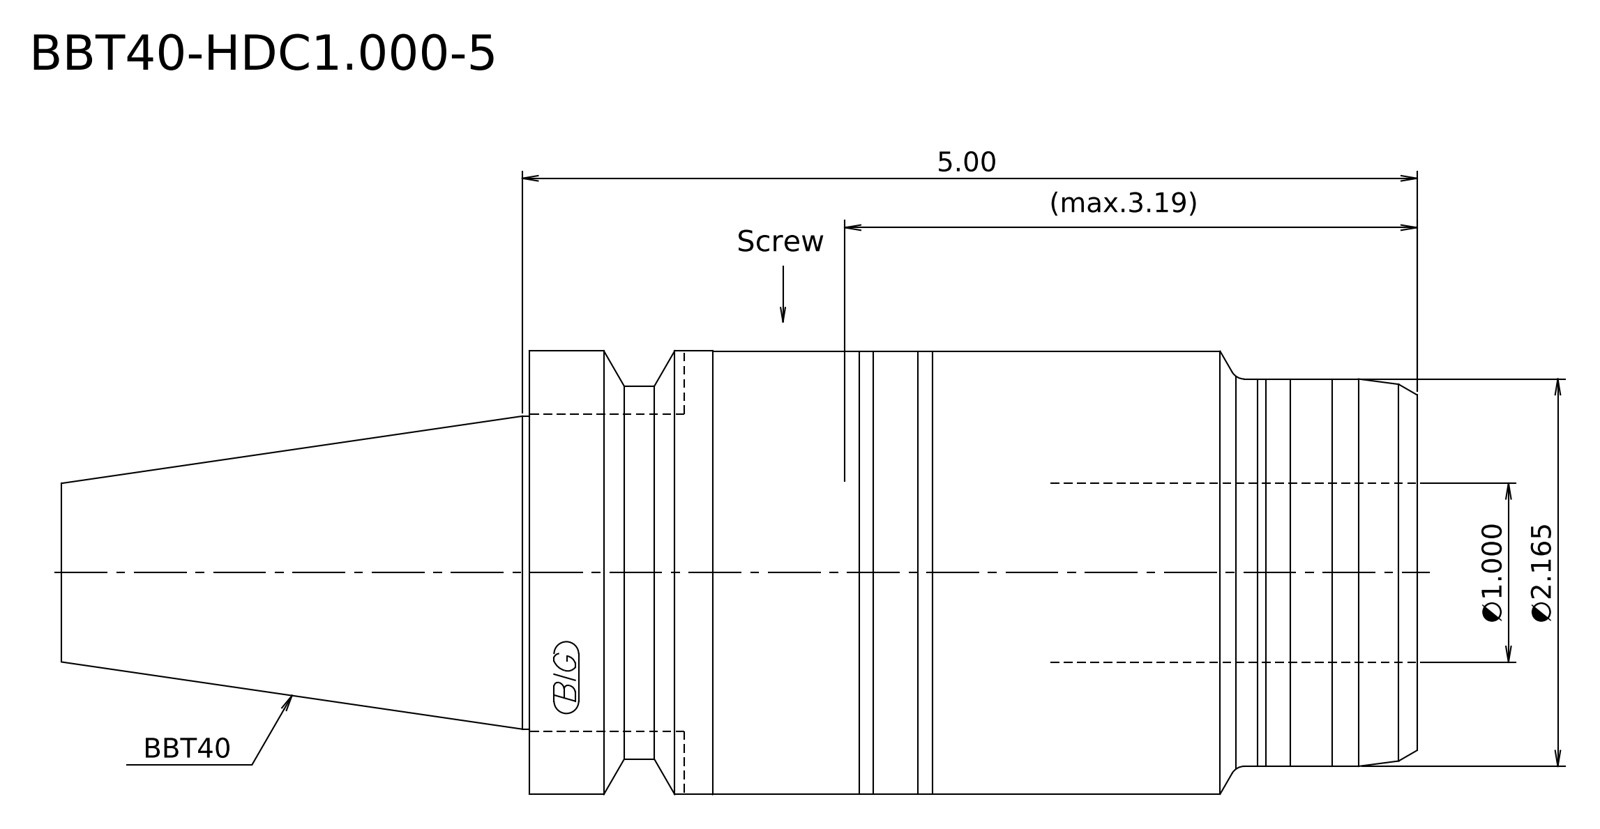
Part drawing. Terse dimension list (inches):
written by: Kubotek KeyCreator 2011 V10.0.2 (22737) (automotive_design)
unit: in
bodies: 1 solid, 15 faces (3 planar, 6 cylindrical, 6 other)
size: 7.575 × 2.48 × 2.48
volume: 26.3 in³; area: 57.43 in²
bosses: 1× ⌀2.48, 1× ⌀2.476, 1× ⌀2.165, 1× ⌀2.087, 1× ⌀1.75
face distances: 4.961, 7.575, 2.614
